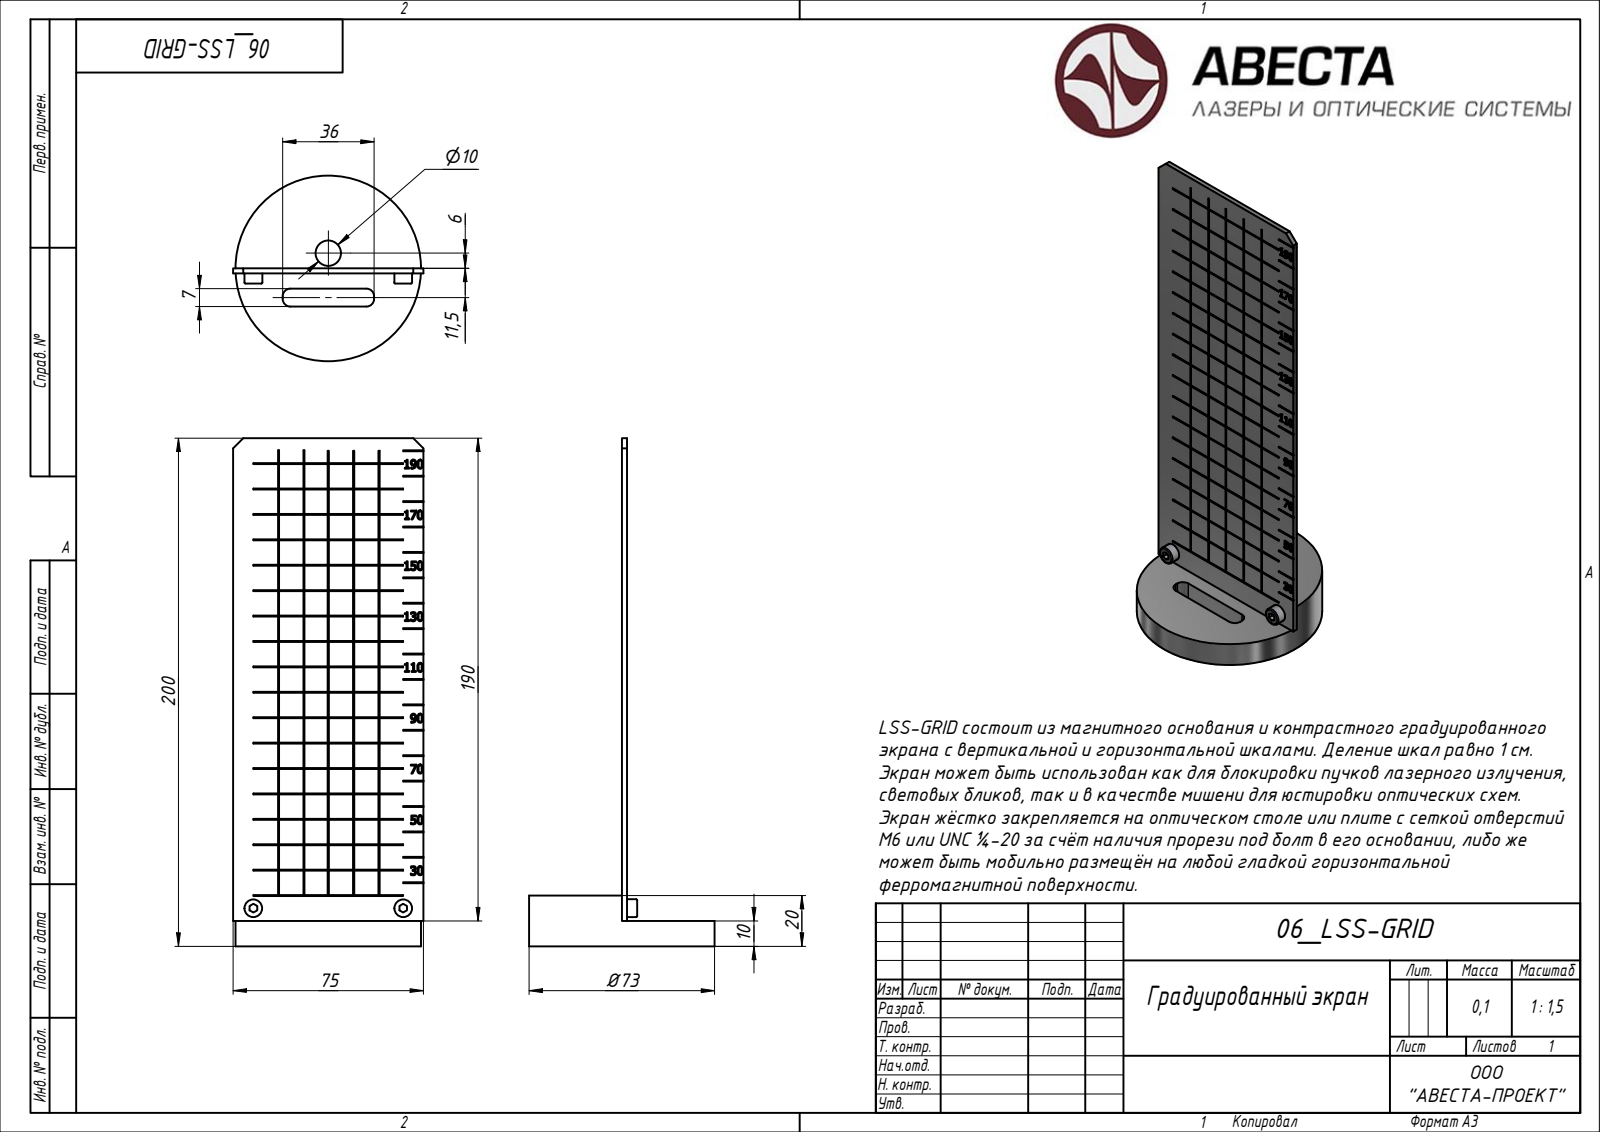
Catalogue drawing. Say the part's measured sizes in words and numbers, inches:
The part is named "06_LSS-GRID; T01_Основание; L01_Экран; DIN 912 - M4 x 0,7 x 10 x 8,25 (+1 more)". Its 3-D file was written by "Autodesk Inventor 2020 (AUTOMOTIVE_DESIGN)". It is 5 solids with 1002 faces: 756 planar, 18 cylindrical and 228 other. Overall it measures 7.874 by 2.953 by 2.874 inches. Its volume is 5.33 cubic inches and its surface area 71.02 square inches. Round holes: 2 of diameter 0.098, 2 of diameter 0.128, 2 of diameter 0.177, 1 of diameter 0.394, 1 of diameter 2.559. Round bosses or shafts: 2 of diameter 0.276, 2 of diameter 0.157, 1 of diameter 2.874. Partial cylindrical surfaces (rounded edges, fillets, slot ends): 4 of radius 0.118. The main face-to-face distances are 0.079, 0.394, 0.78, 0.386, 0.787, 0.067, 2.953, 0.236, 0.315, 0.512. The hole center spacings are 2.323, 0.236, 1.172, 1.174, 1.226, 1.232.
